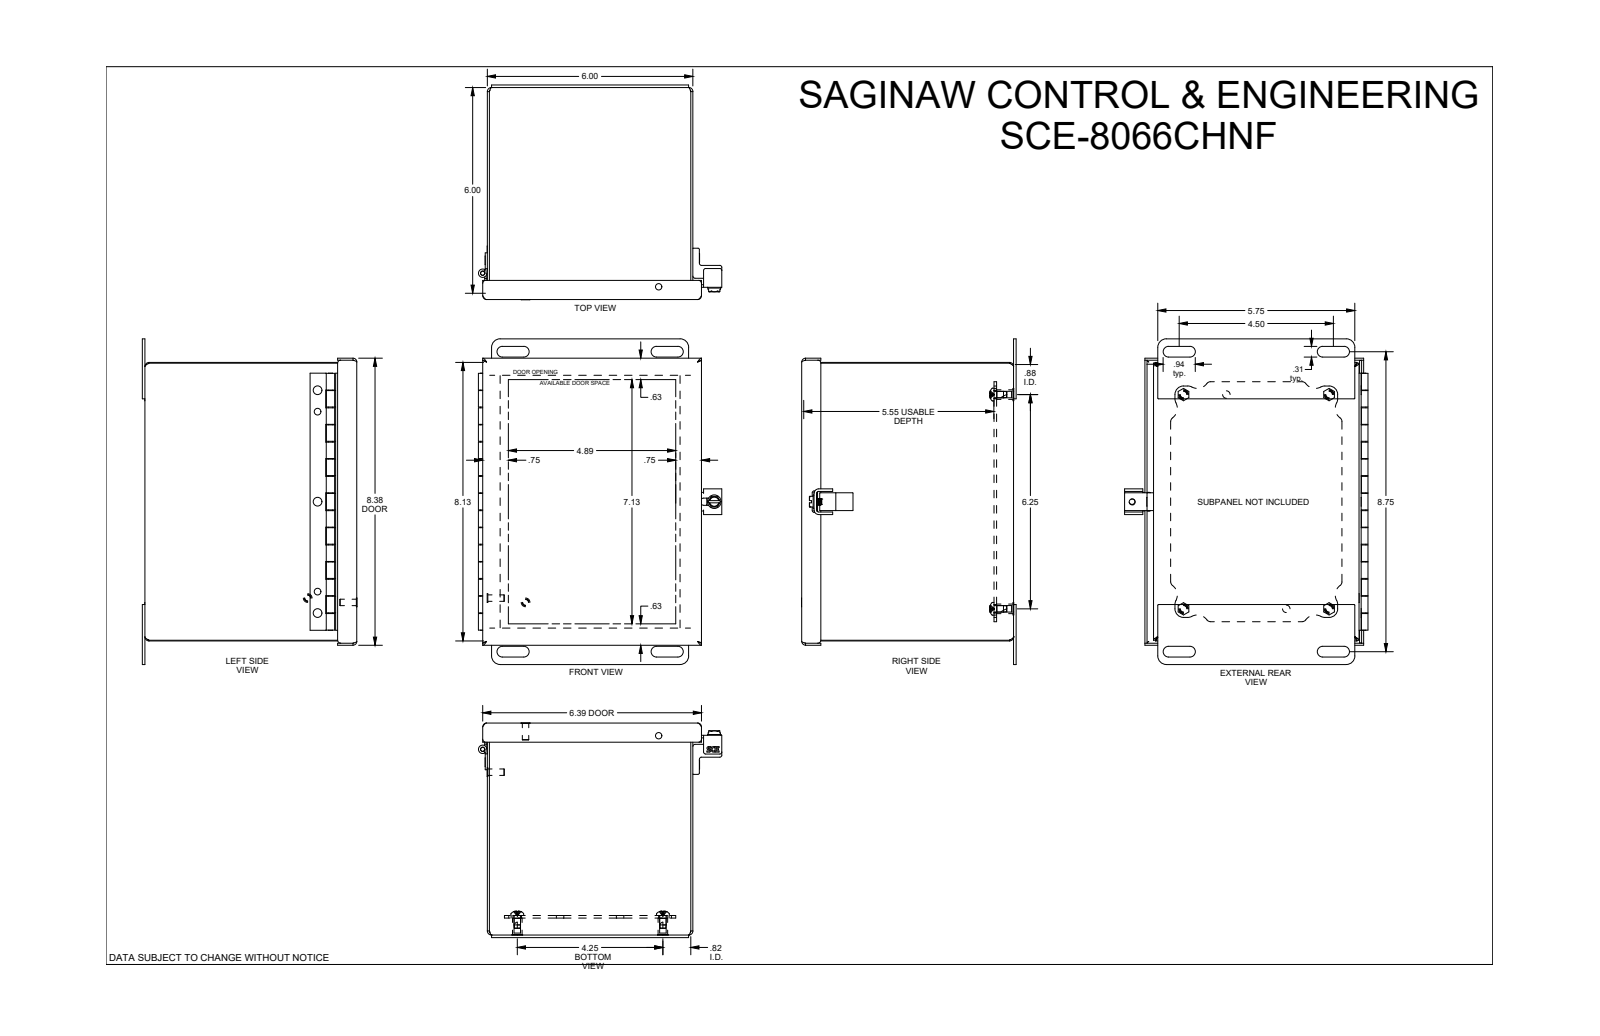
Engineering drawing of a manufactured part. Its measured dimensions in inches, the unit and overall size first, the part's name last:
Units: inches
Overall size (bounding box): 9.5 × 7.104 × 6.265
Round holes (diameter × count): ⌀0.19 ×8, ⌀0.193 ×6, ⌀0.25 ×4, ⌀0.281 ×4, ⌀0.193 ×2, ⌀0.218 ×2, ⌀0.126 ×1, ⌀0.156 ×1, ⌀0.187 ×1, ⌀0.266 ×1
Round bosses / shafts (diameter × count): ⌀0.188 ×11, ⌀0.256 ×6, ⌀0.373 ×4, ⌀0.28 ×4, ⌀0.396 ×1, ⌀0.246 ×1, ⌀0.123 ×1
Partial cylindrical surfaces — rounded edges, fillets, slot ends (radius × count): R0.01 ×56, R0.25 ×16, R0.06 ×13, R0.052 ×8, R0.112 ×8, R0.125 ×8, R0.156 ×8, R0.344 ×8
Main face-to-face distances: 0.06, 5.94, 0.06, 6.125, 6, 5.88, 6.185, 6.125, 6.065, 0.075
Hole centre spacings: 1.25, 3, 3.25, 3.251, 4.25, 6.25, 6.374, 6.933
Bodies: 0 solids, 1091 faces (500 planar, 293 cylindrical, 298 other)
Part name (STEP PRODUCT): SCE-8066CHNF
STEP written by: SolidWorks 2019 (CONFIG_CONTROL_DESIGN)
